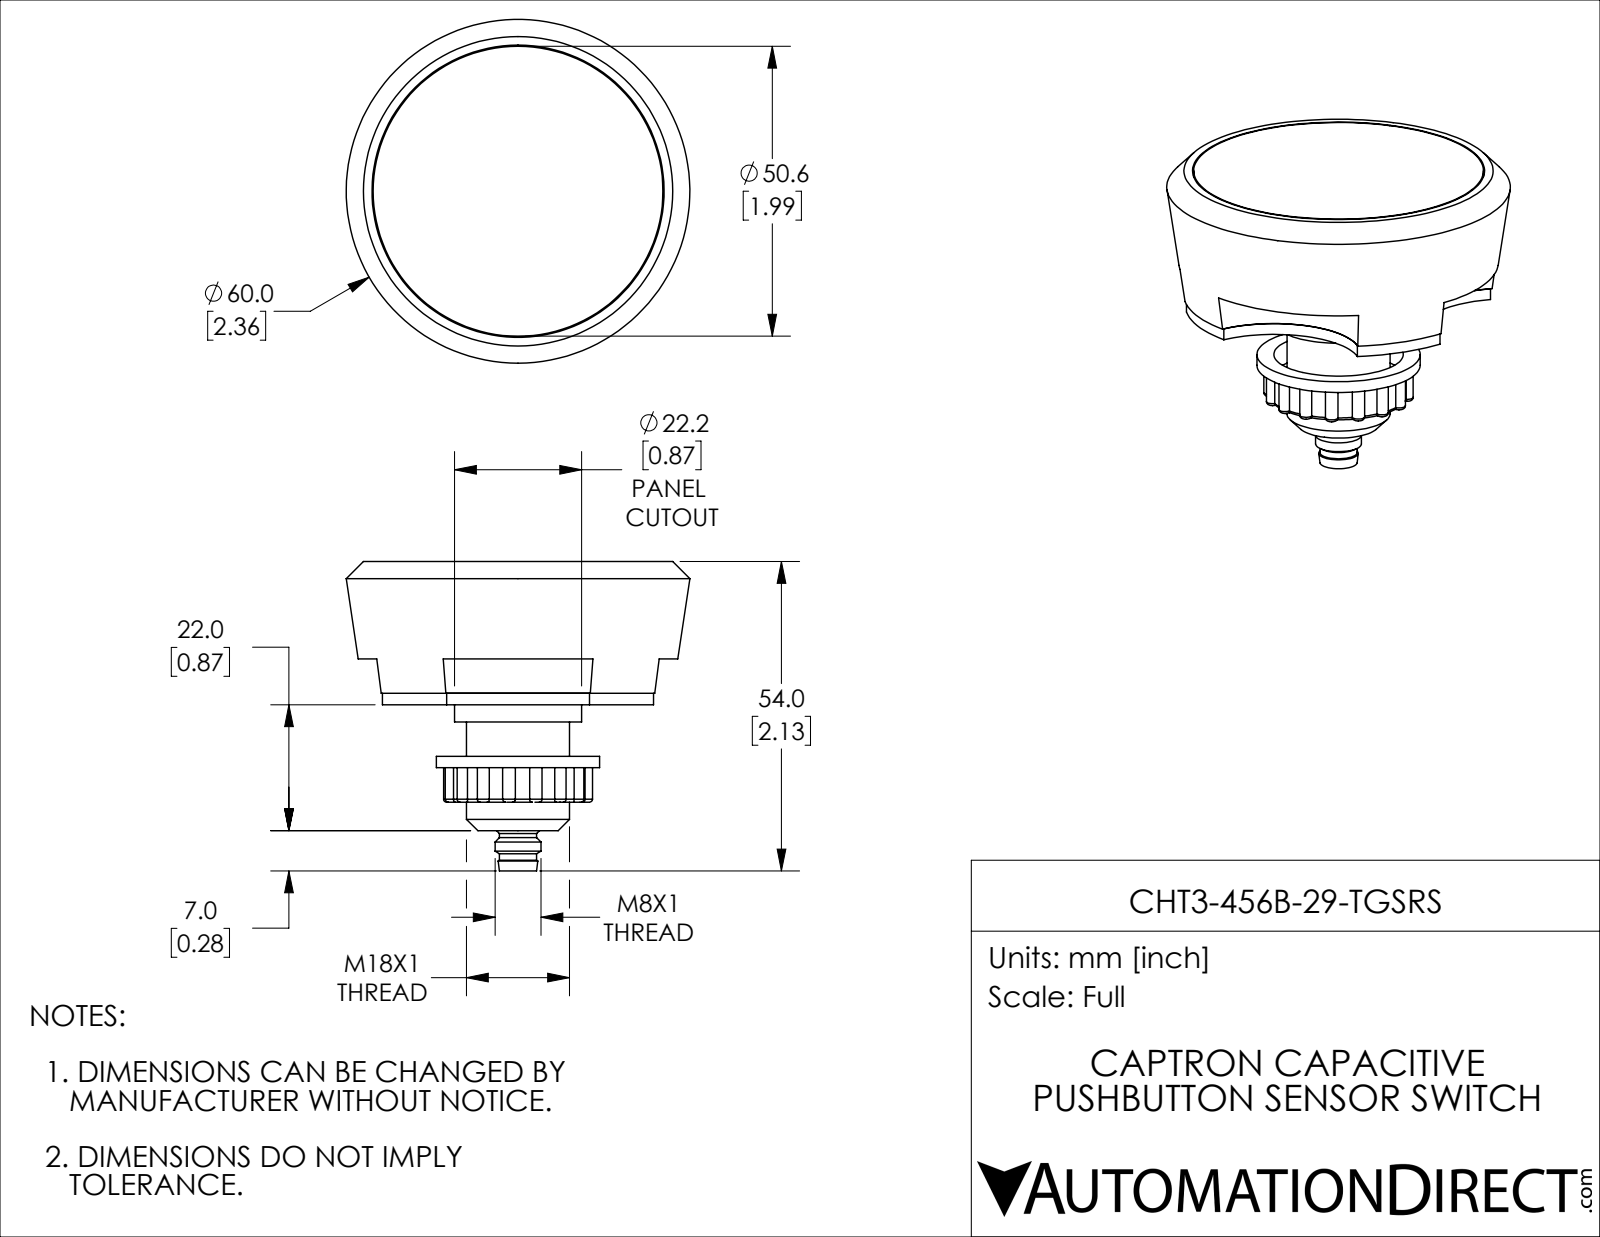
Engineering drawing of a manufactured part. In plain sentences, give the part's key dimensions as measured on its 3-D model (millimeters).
The part is named "CHT3-456B-29-TGSRS". Its 3-D file was written by "SolidWorks 2019 (CONFIG_CONTROL_DESIGN)". It is 10 solids with 200 faces: 28 planar, 94 cylindrical and 78 other. Overall it measures 60 by 60 by 54 millimeters. Its volume is 63 140 cubic millimeters and its surface area 20 940 square millimeters. Round holes: 1 of diameter 17, 1 of diameter 22.6, 1 of diameter 51. Round bosses or shafts: 5 of diameter 1, 1 of diameter 50.6, 1 of diameter 28.5, 1 of diameter 22.2, 1 of diameter 18, 1 of diameter 8, 1 of diameter 6.5. Partial cylindrical surfaces (rounded edges, fillets, slot ends): 16 of radius 1.1, 4 of radius 15, 2 of radius 0.5, 1 of radius 1, 1 of radius 2.9, 1 of radius 12, 1 of radius 26.7. The main face-to-face distances are 23, 2.3, 20.7, 3.4, 19.6, 1.1, 2, 25, 17, 21.6.
